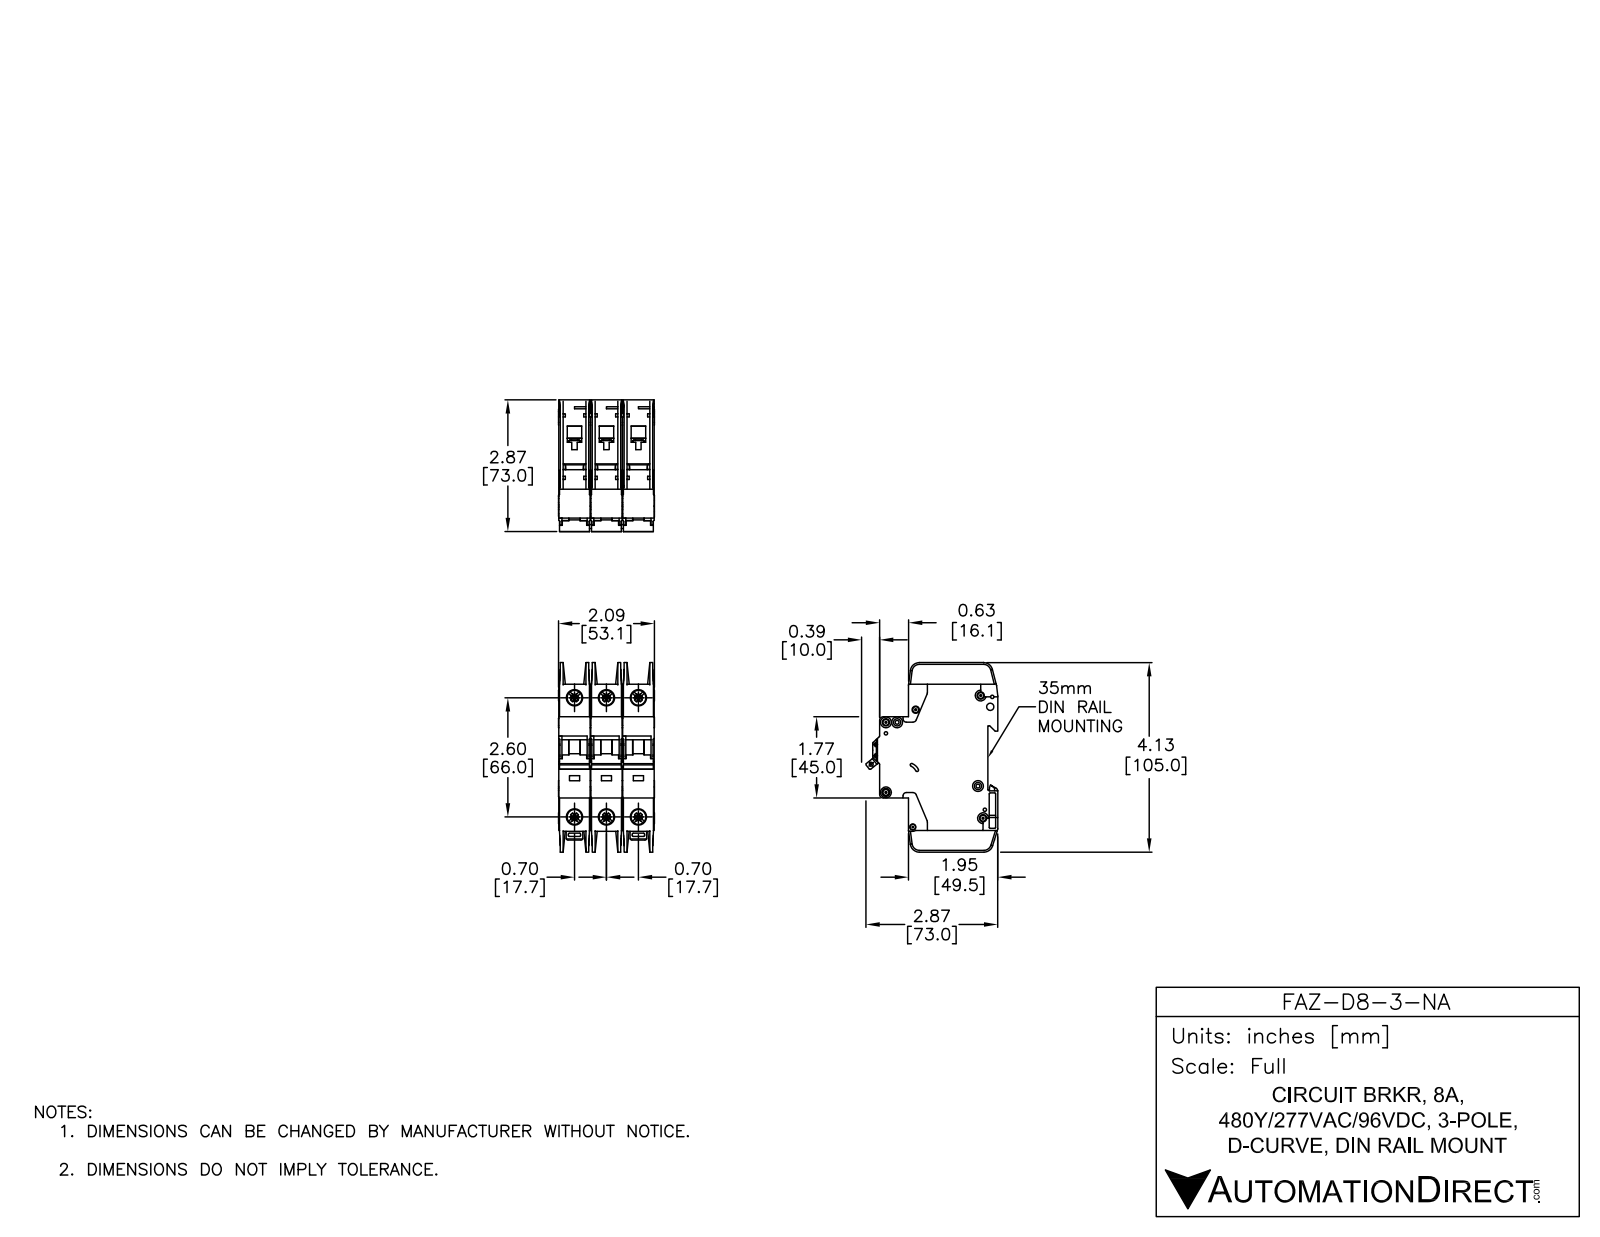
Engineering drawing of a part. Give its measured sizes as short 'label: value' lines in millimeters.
name: FAZ-D8-3-NA
written by: SolidWorks 2014 (AUTOMOTIVE_DESIGN)
unit: mm
bodies: 9 solids, 2352 faces (1227 planar, 789 cylindrical, 336 other)
size: 105 × 73.04 × 53.1
volume: 233 085 mm³; area: 74 219 mm²
holes: 7× ⌀3.6, 6× ⌀7.15, 6× ⌀8.2, 2× ⌀1.09, 2× ⌀1.5, 2× ⌀4, 1× ⌀1.9, 1× ⌀2.15, 1× ⌀2.2, 1× ⌀2.55, 1× ⌀3.3, 1× ⌀3.4
bosses: 7× ⌀6, 3× ⌀2.5
rounds: 65× R0.25, 30× R0.5, 26× R1, 14× R2, 5× R1.8, 5× R5, 4× R4, 2× R0.2
face distances: 17.7, 35.4, 17.5, 35.2, 0.7, 15.05, 2.45, 1.75, 15.75, 13.3
hole spacings: 17.7, 68.33, 66, 6.2, 35.4, 74.89, 5.19, 6.1
